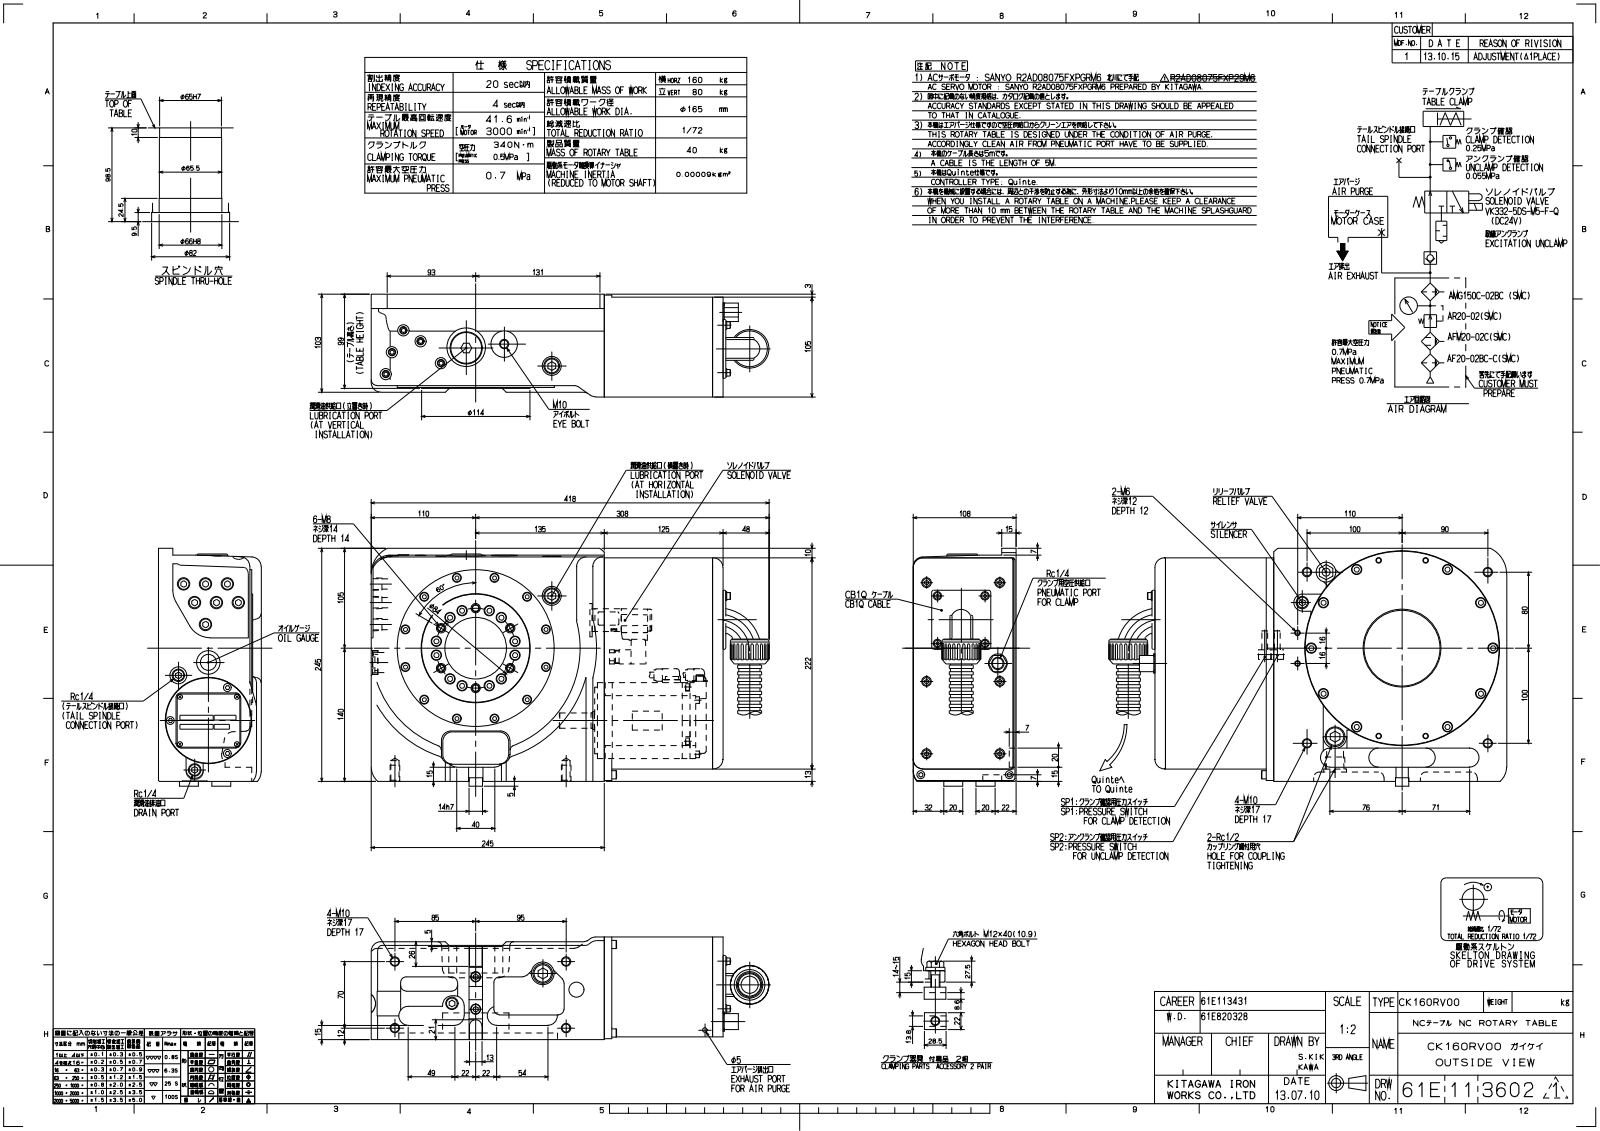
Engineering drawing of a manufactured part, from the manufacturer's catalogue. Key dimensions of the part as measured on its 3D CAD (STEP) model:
Part name (STEP PRODUCT): RlN^Jo[i61E3639681jMR160RAF02; B p[J@M12~40; OUTSIDE VIEW-CKR160RZ01
STEP written by: SolidWorks 2014 (CONFIG_CONTROL_DESIGN)
Units: millimetres
Bodies: 11 solids, 3051 faces (1713 planar, 811 cylindrical, 527 other)
Overall size (bounding box): 457 × 267 × 221
Volume: 10 520 000 mm³ · Surface area: 647 318 mm²
Round holes (diameter × count): ⌀6 ×24, ⌀6.6 ×24, ⌀11 ×24, ⌀5.5 ×15, ⌀9.5 ×15, ⌀3 ×11, ⌀8 ×10, ⌀10 ×10, ⌀8.5 ×9, ⌀5 ×8, ⌀12 ×7, ⌀10.5 ×6
Round bosses / shafts (diameter × count): ⌀10 ×30, ⌀8.5 ×26, ⌀6 ×22, ⌀12 ×4, ⌀9 ×4, ⌀5.5 ×4, ⌀7 ×3, ⌀25 ×2
Partial cylindrical surfaces — rounded edges, fillets, slot ends (radius × count): R10 ×29, R6 ×20, R0.2 ×16, R0.4 ×12, R0.6 ×12, R8.65 ×6, R11.35 ×6, R3 ×4
Main face-to-face distances: 3, 105, 1.6, 2.5, 107.5, 5, 118.4, 0.5, 6, 2
Hole centre spacings: 76.5, 39.6, 108.18, 147.78, 76.49, 87.56, 122.36, 132.49
